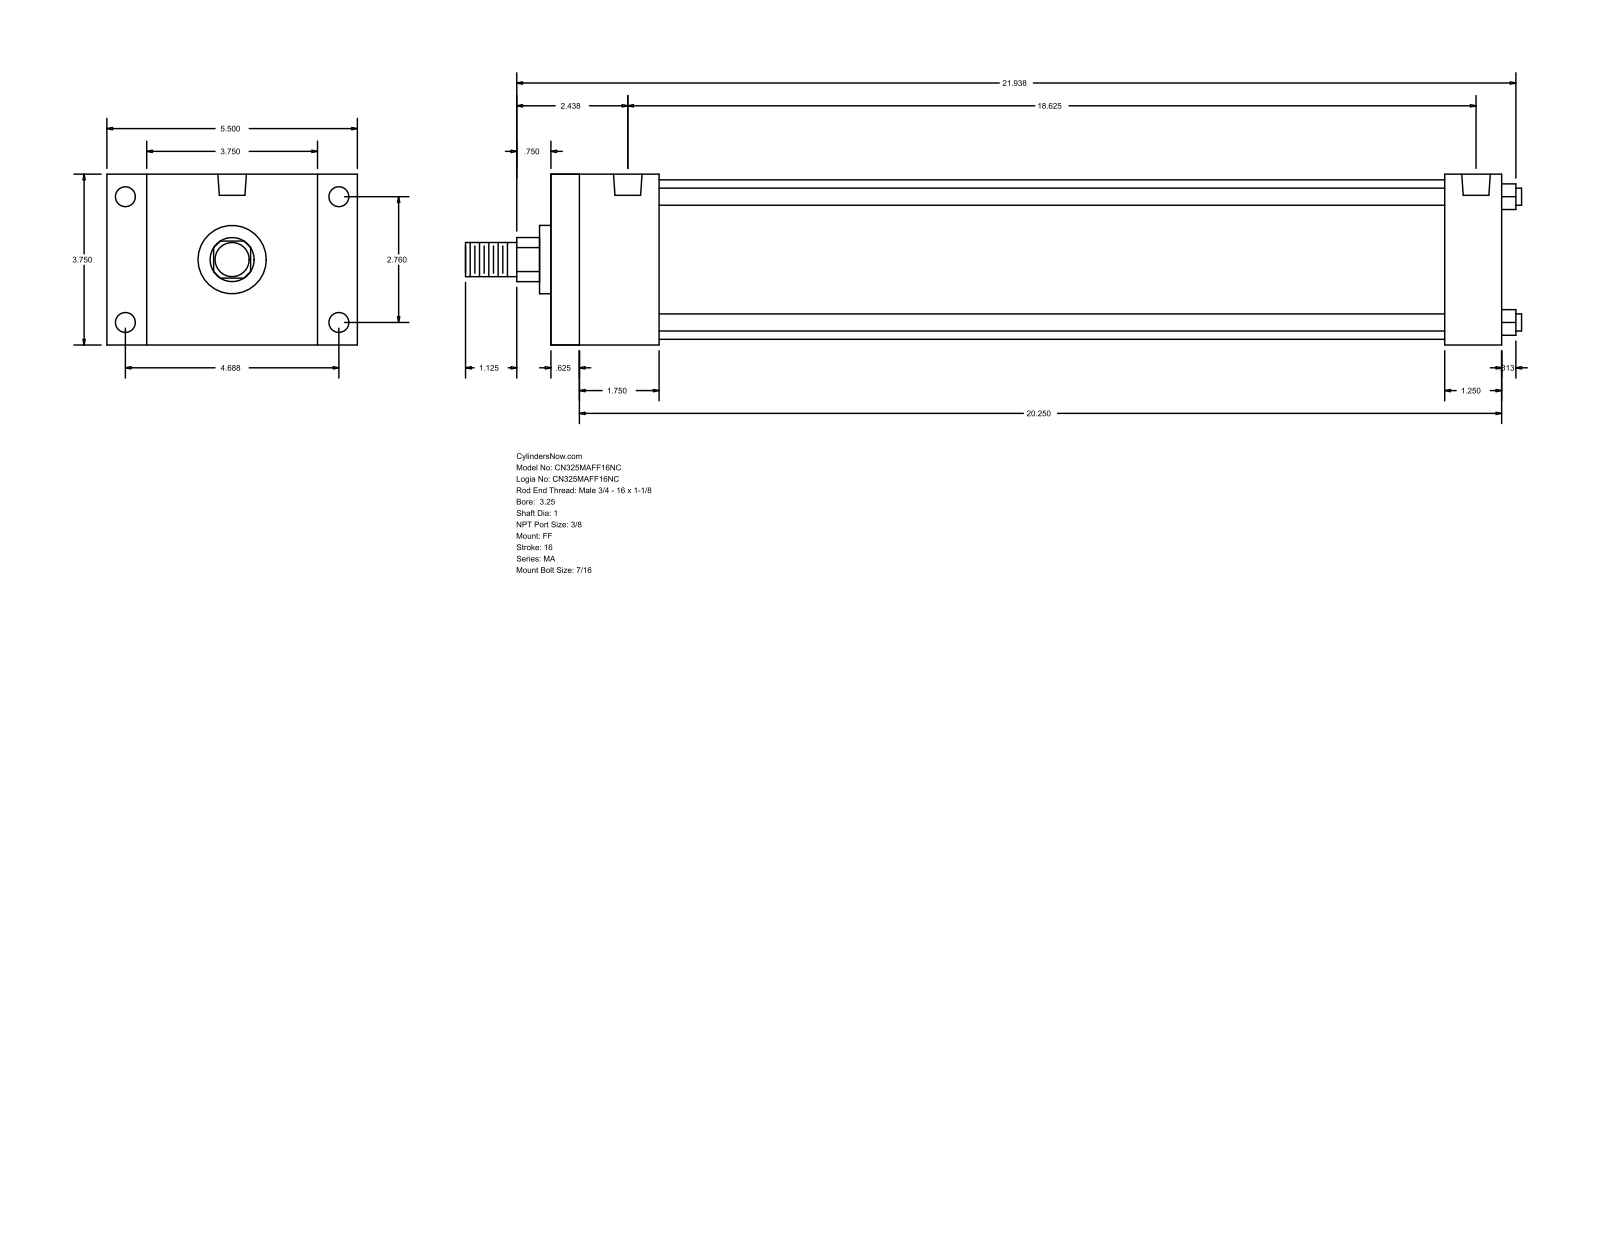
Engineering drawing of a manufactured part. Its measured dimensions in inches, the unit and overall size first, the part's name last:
Units: inches
Overall size (bounding box): 23.187 × 5.5 × 3.75
Round holes (diameter × count): ⌀0.437 ×8, ⌀0.627 ×2
Round bosses / shafts (diameter × count): ⌀0.375 ×4, ⌀3.5 ×1, ⌀1.5 ×1, ⌀1 ×1, ⌀0.75 ×1
Partial cylindrical surfaces — rounded edges, fillets, slot ends (radius × count): R0.484 ×1
Main face-to-face distances: 3.75, 20.875, 0.625, 20.25, 0.875, 4.625, 2.375, 19.625, 1.75, 19
Hole centre spacings: 0.187, 2.76, 4.687, 5.439, 18.25, 18.438, 18.625
Bodies: 0 solids, 92 faces (64 planar, 28 cylindrical, 0 other)
Part name (STEP PRODUCT): MA_FF__0325_1
STEP written by: GSSL Pune (CONFIG_CONTROL_DESIGN)
